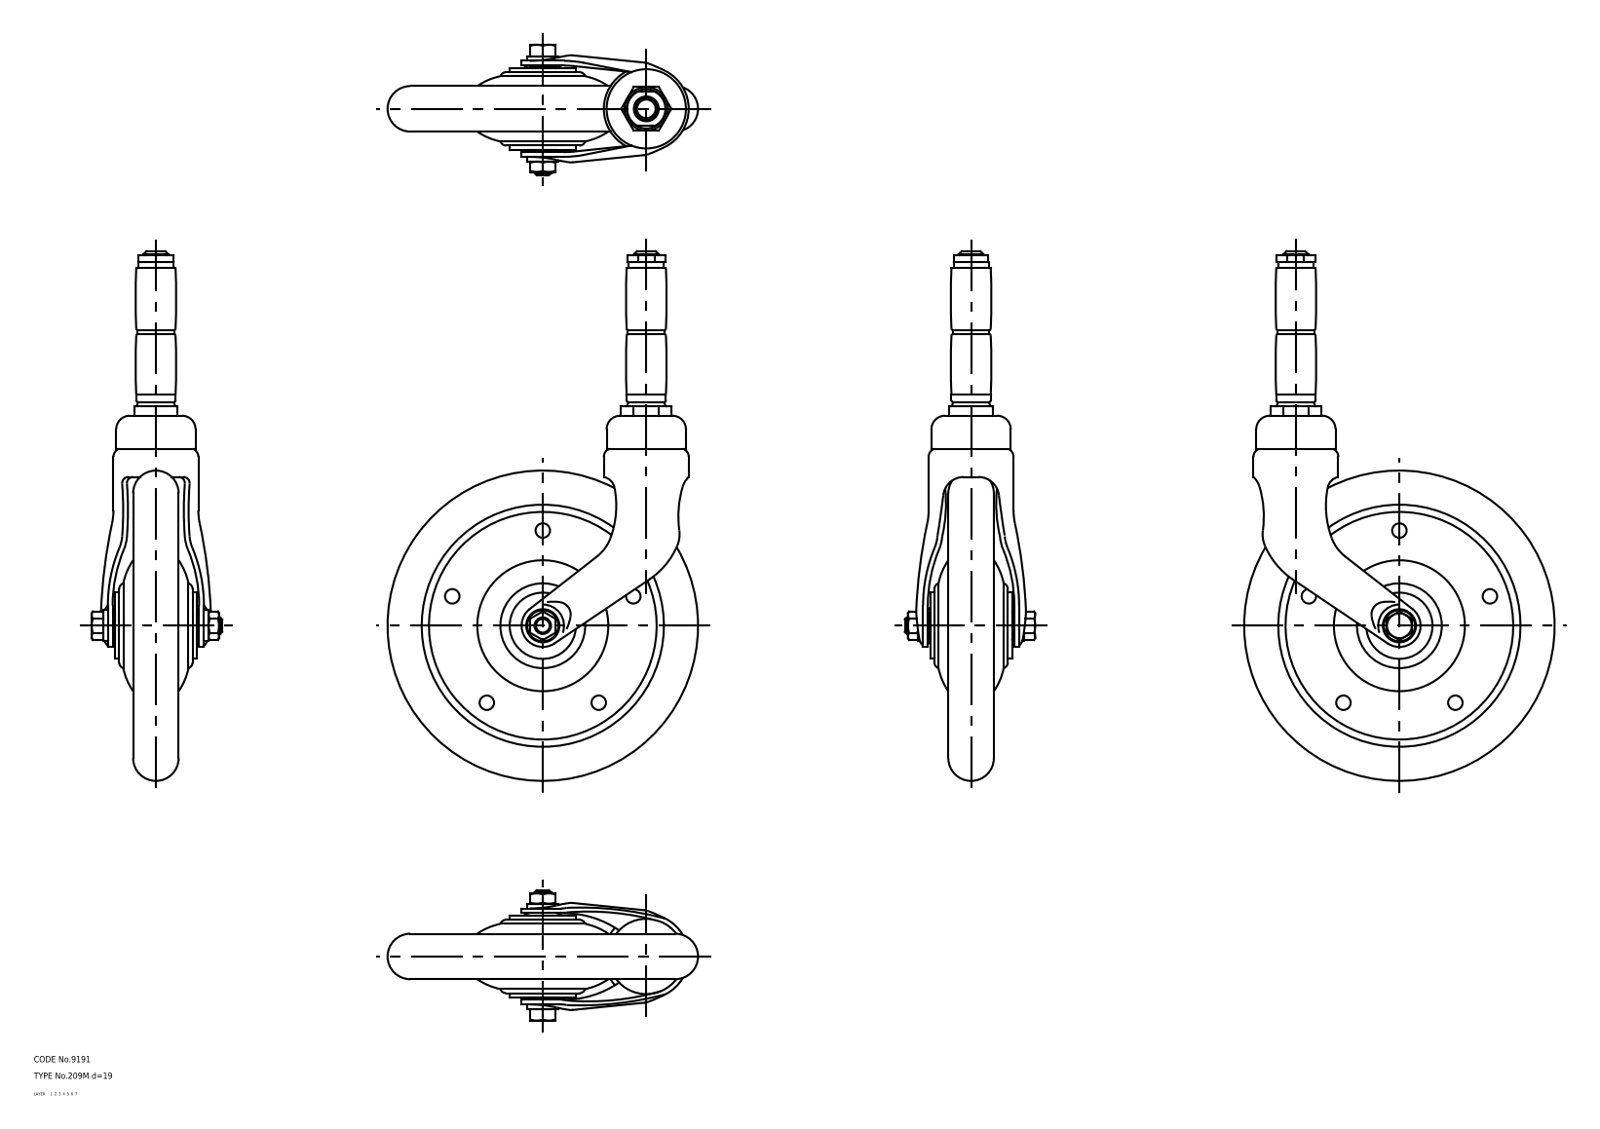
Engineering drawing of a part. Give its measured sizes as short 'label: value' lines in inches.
name: wheel; main shaft; axle; No_209M_d19_6431_36
written by: CADfix (AUTOMOTIVE_DESIGN)
unit: in
bodies: 4 solids, 301 faces (0 planar, 0 cylindrical, 301 other)
size: 10.079 × 5.906 × 2.48
volume: 22.31 in³; area: 126.9 in²
